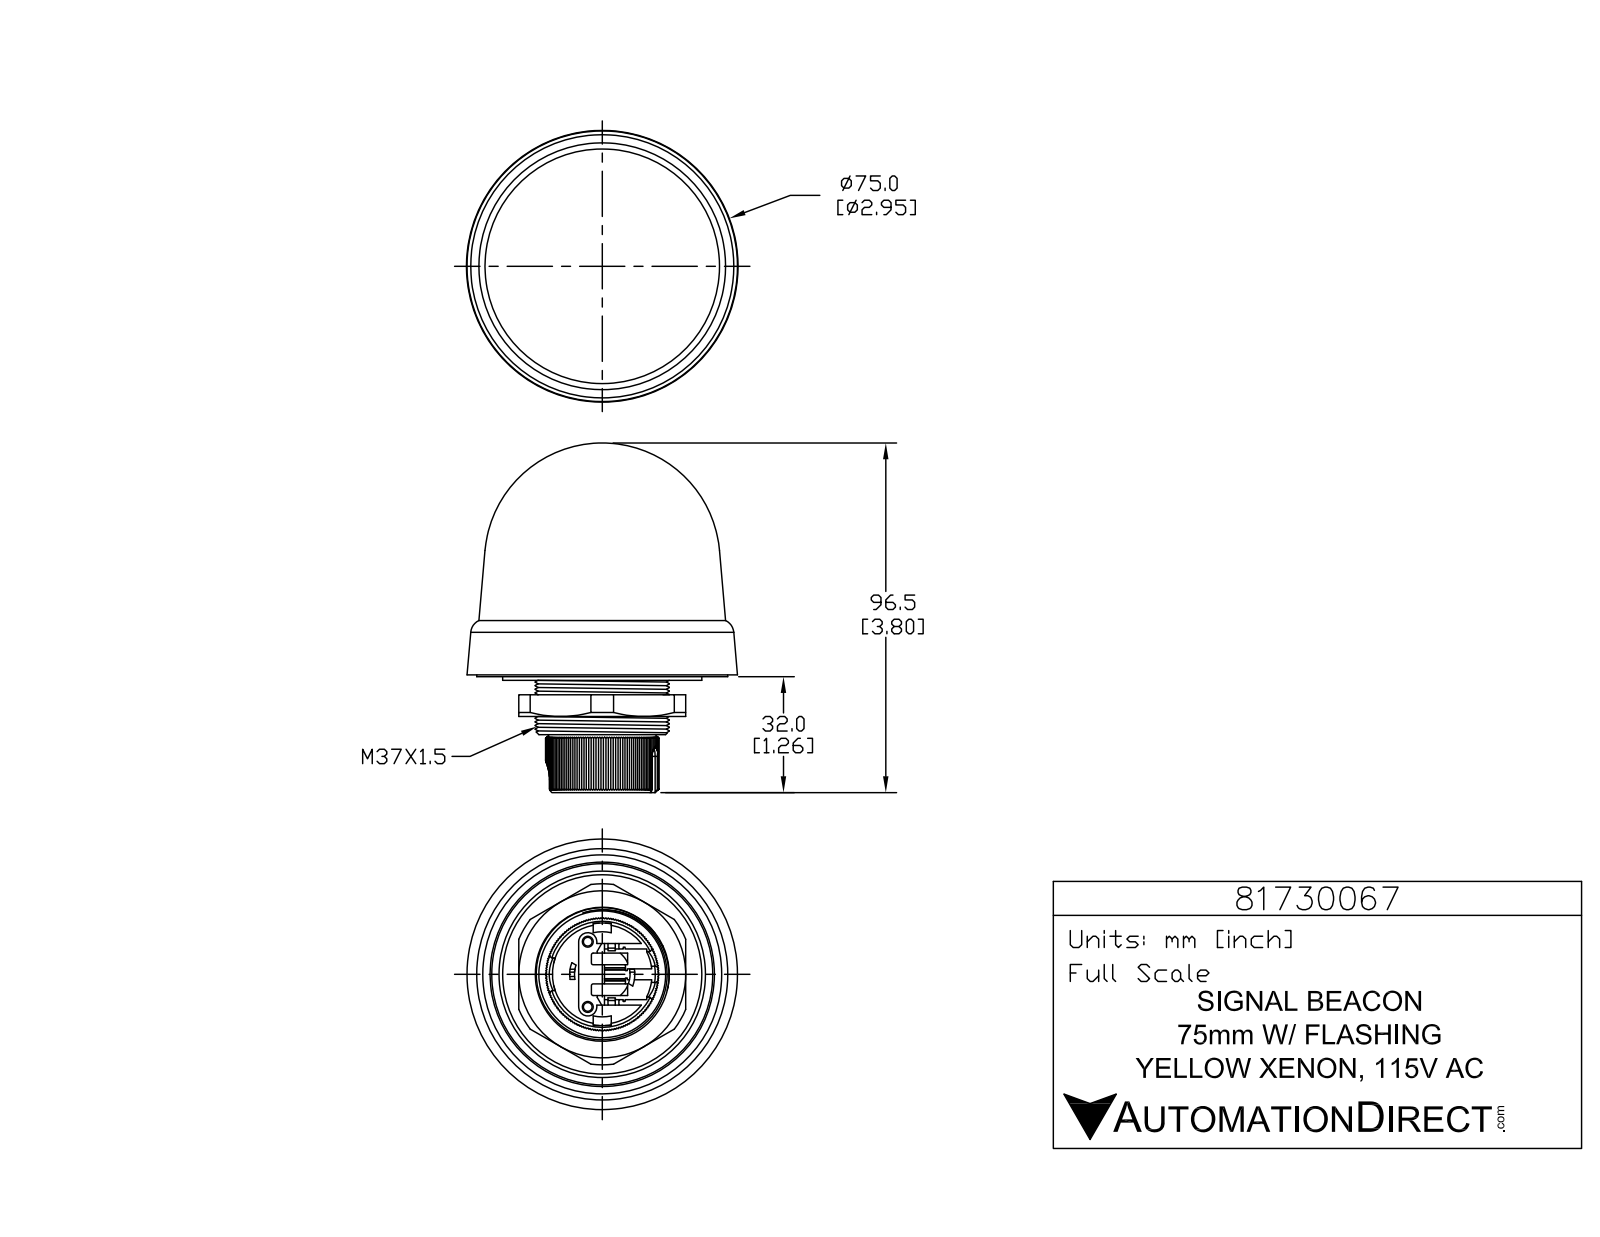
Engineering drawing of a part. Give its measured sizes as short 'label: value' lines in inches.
name: 81730067
written by: SolidWorks 2019 (CONFIG_CONTROL_DESIGN)
unit: in
bodies: 3 solids, 560 faces (432 planar, 80 cylindrical, 48 other)
size: 3.799 × 2.941 × 2.941
volume: 12.36 in³; area: 58.68 in²
holes: 2× ⌀0.094, 2× ⌀0.118, 1× ⌀0.604, 1× ⌀1.142
bosses: 2× ⌀0.217, 2× ⌀0.067, 1× ⌀2.165, 1× ⌀1.457, 1× ⌀0.925
rounds: 6× R0.008, 6× R0.039, 4× R0.02, 2× R0.031, 2× R0.079, 2× R0.098, 1× R0.177, 1× R0.354
face distances: 0.177, 0.354, 0.197, 0.433, 0.512, 0.335, 0.059, 0.394, 0.118, 0.157
hole spacings: 0.388, 0.709
